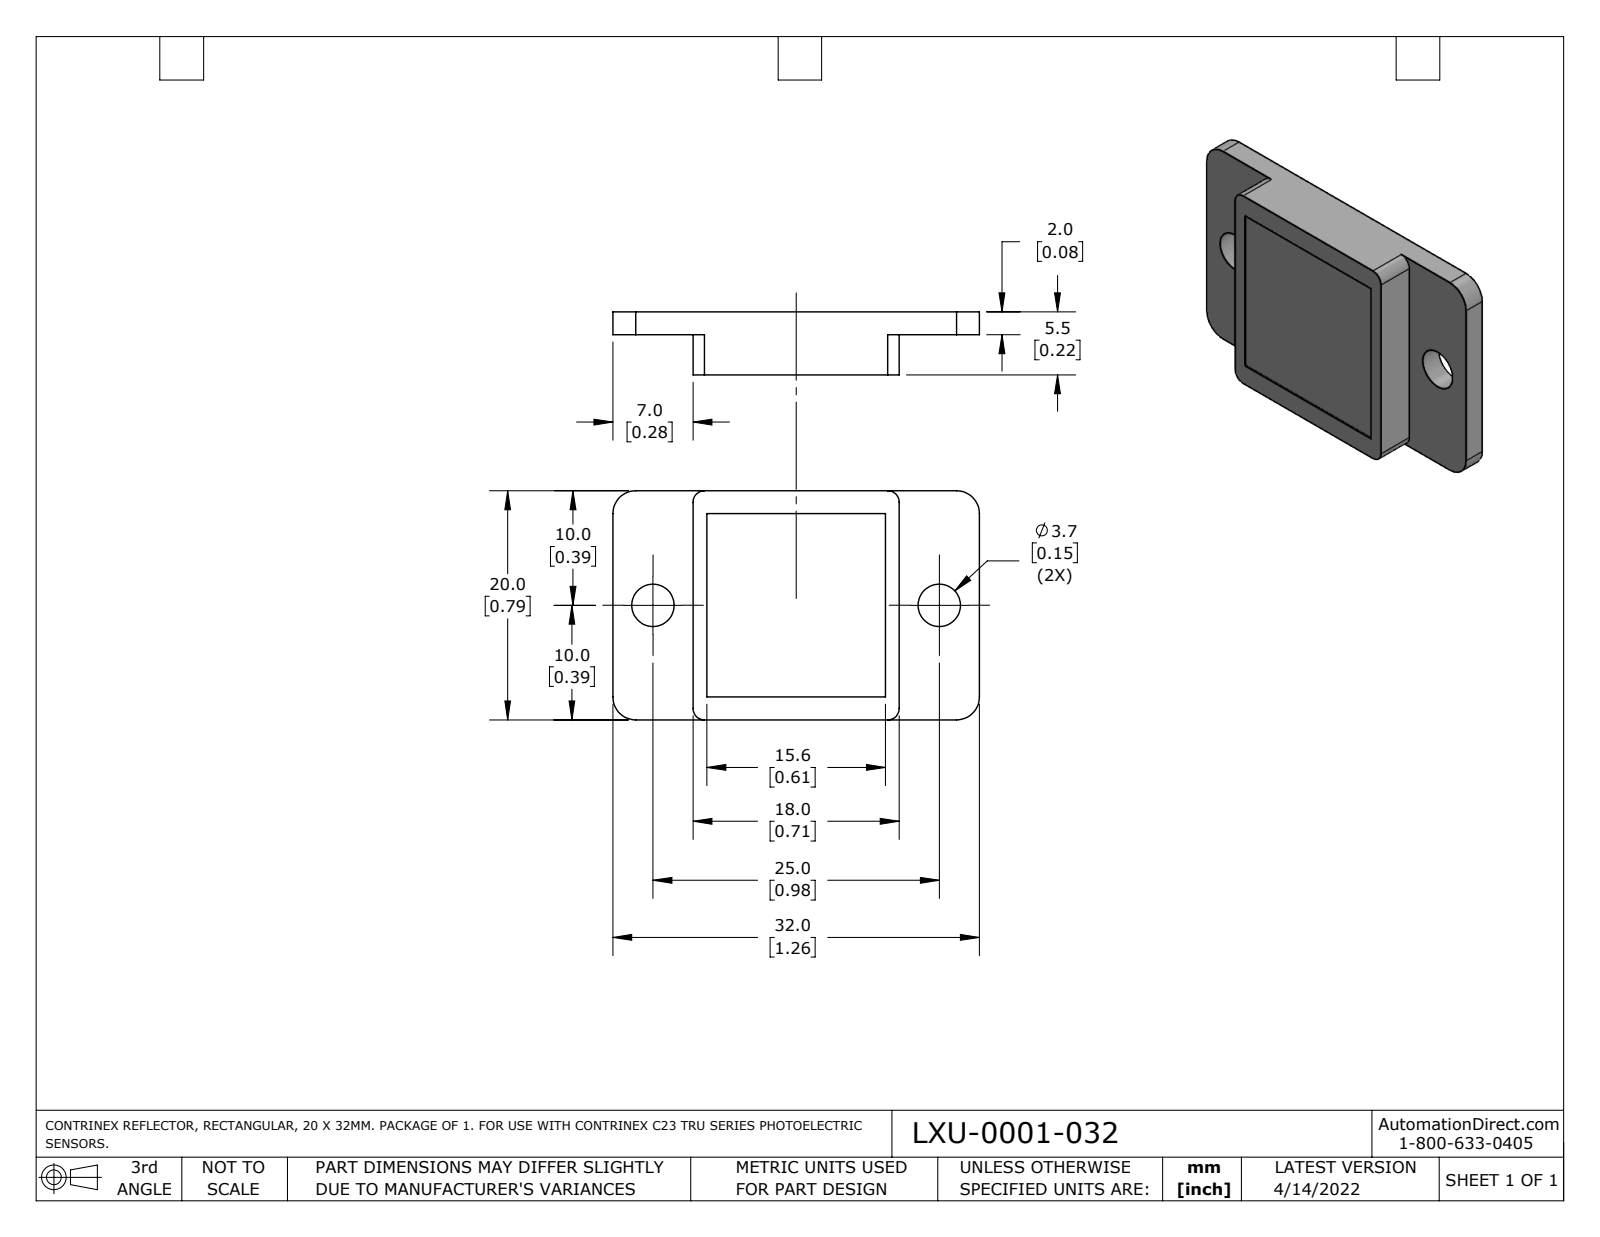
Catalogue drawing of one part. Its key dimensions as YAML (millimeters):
part_name: "LXU-0001-032"
step_written_by: "PARTsolutions (AUTOMOTIVE_DESIGN)"
units: millimeters
bodies: {solids: 1, faces: 25, planar: 15, cylindrical: 10, other: 0}
overall_size: [32, 20, 5.5]
volume: 2462
surface_area: 1744
round_holes:
  - {diameter: 3.7, count: 2}
partial_cylinders:
  - {radius: 1, count: 4}
  - {radius: 2, count: 4}
face_to_face_distances: [2, 5.4, 3.4, 20, 5.5, 3.5, 18, 7, 25, 32]
hole_center_spacings: [25]
